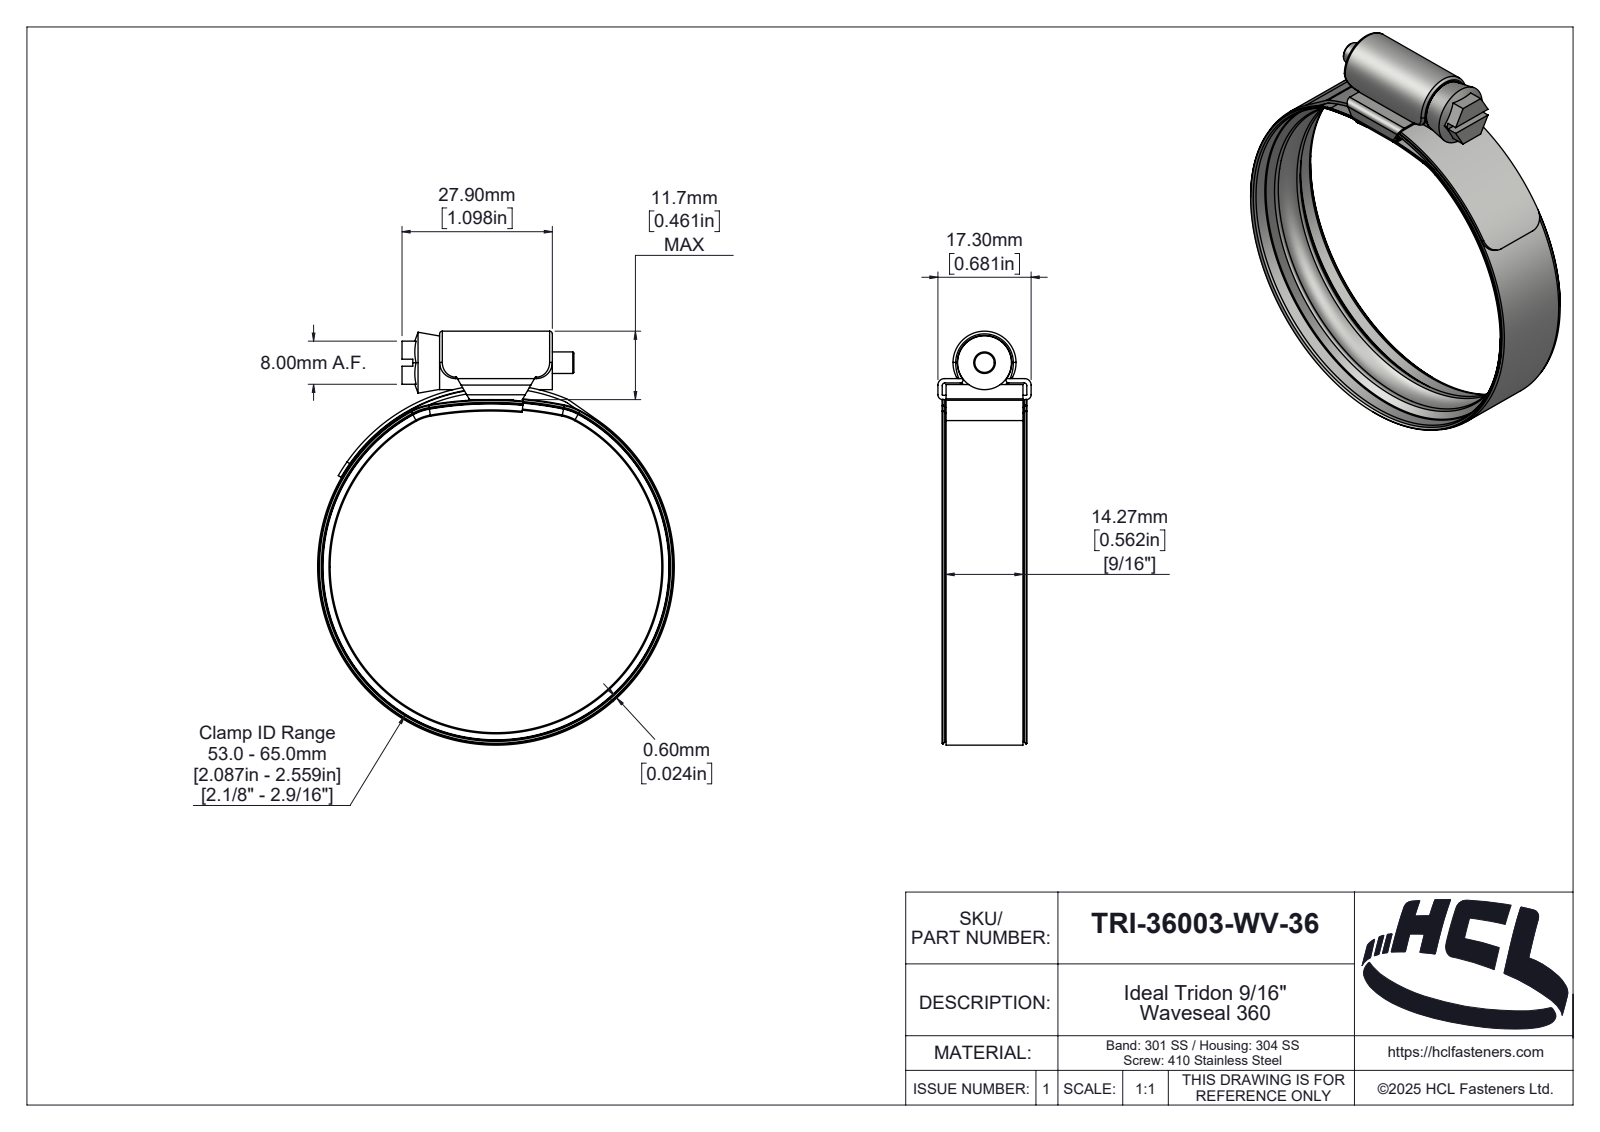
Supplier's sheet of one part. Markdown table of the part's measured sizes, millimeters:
| quantity | value |
| --- | --- |
| part name | TRI-36003-WV-36 |
| STEP written by | SolidWorks 2025 (AUTOMOTIVE_DESIGN) |
| units | millimeters |
| bodies | 4 solids, 418 faces (42 planar, 119 cylindrical, 257 other) |
| overall size | 76.8 × 66.2 × 17.3 |
| volume | 5 657 mm³ |
| surface area | 17 490 mm² |
| round holes (diameter × count) | 64.4 × 1, 65 × 1 |
| round bosses / shafts (diameter × count) | 66.2 × 1, 64.8 × 1, 10 × 1, 4 × 1 |
| partial cylindrical surfaces (radius × count) | 0.5 × 6, 3 × 4, 0.1 × 2, 0.9 × 2, 1.2 × 2, 9.9 × 2, 10.1 × 2, 0.46 × 1 |
| main face-to-face distances | 0.8, 3.1, 14.26, 0.6, 2.3, 3.9, 27.9, 1.52, 15.78, 16.5 |
